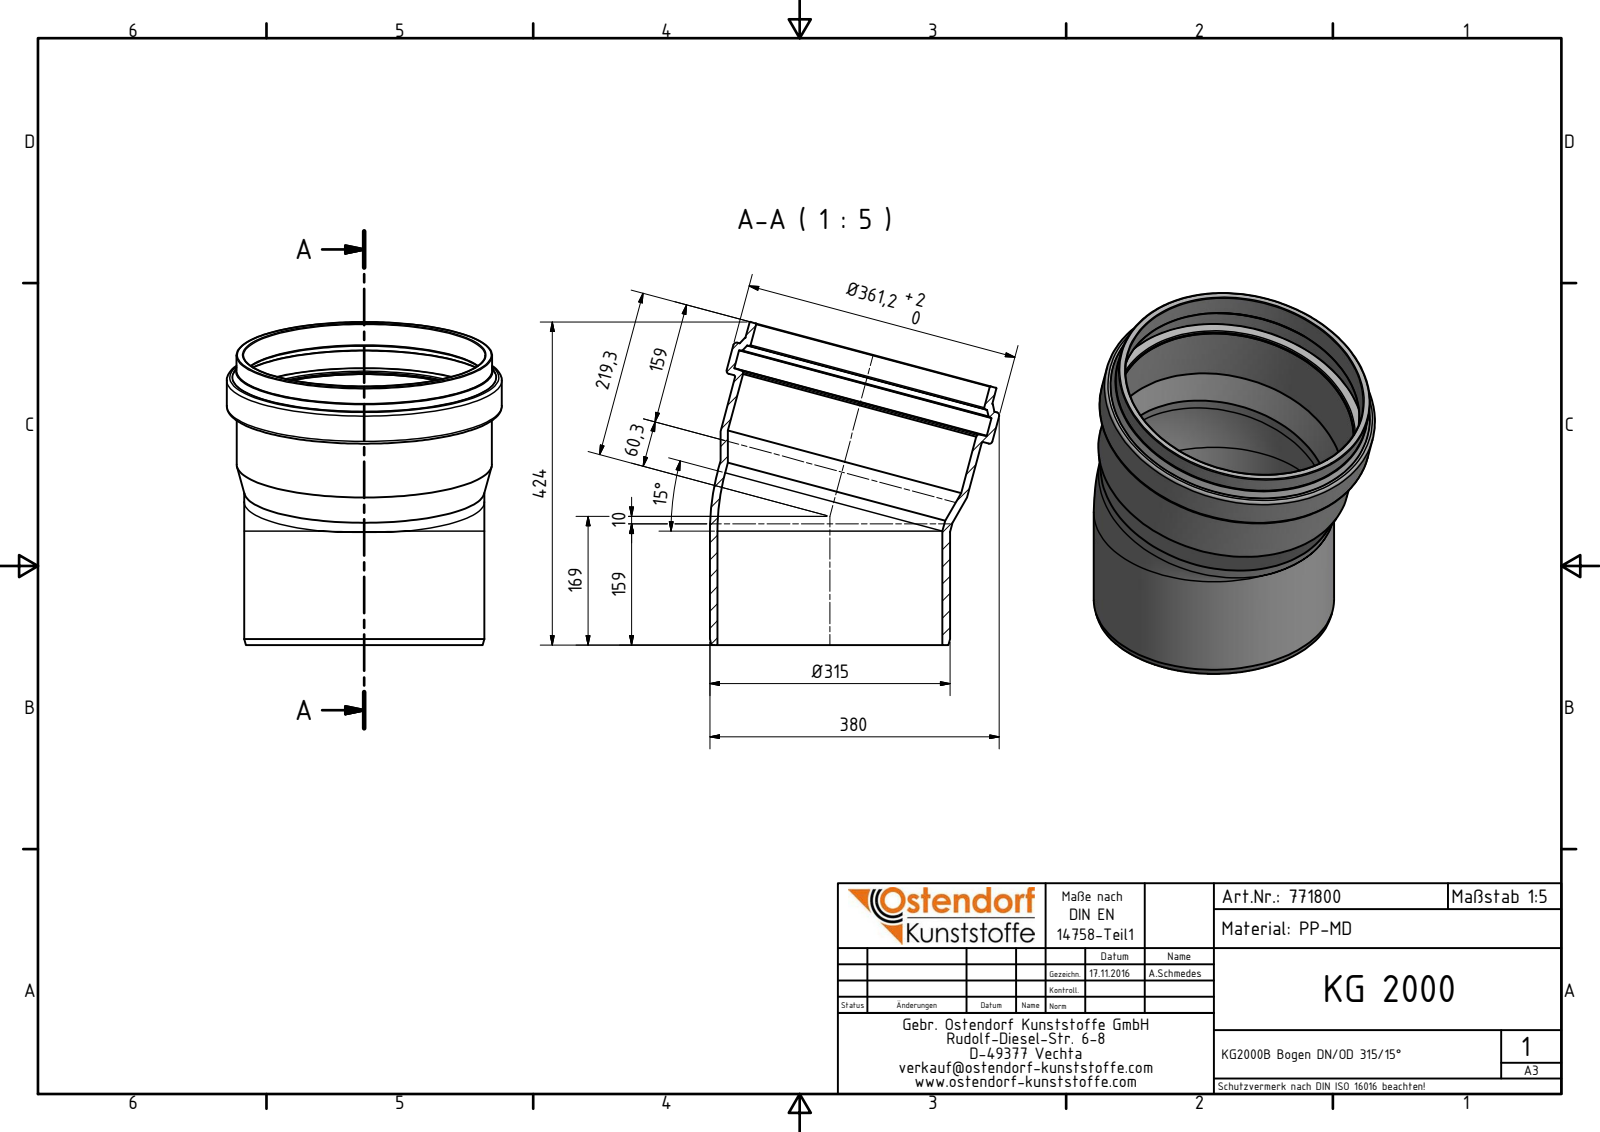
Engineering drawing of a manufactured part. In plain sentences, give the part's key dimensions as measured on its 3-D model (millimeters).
The part is named "771800 KG2000B Bogen DN_OD 315_15°". Its 3-D file was written by "Autodesk Inventor 2016 (AUTOMOTIVE_DESIGN)". It is 1 solid with 41 faces: 5 planar, 11 cylindrical and 25 other. Overall it measures 424 by 380 by 361.2 millimeters. Its volume is 3 864 000 cubic millimeters and its surface area 830 626 square millimeters. Round holes: 2 of diameter 295.3, 2 of diameter 317.5, 1 of diameter 317.1, 1 of diameter 343.2. Round bosses or shafts: 2 of diameter 315.3, 1 of diameter 361.2, 1 of diameter 335.5, 1 of diameter 335.1. The main face-to-face distances are 73.1, 42.4, 30.7, 4.55, 37.85, 68.55.
